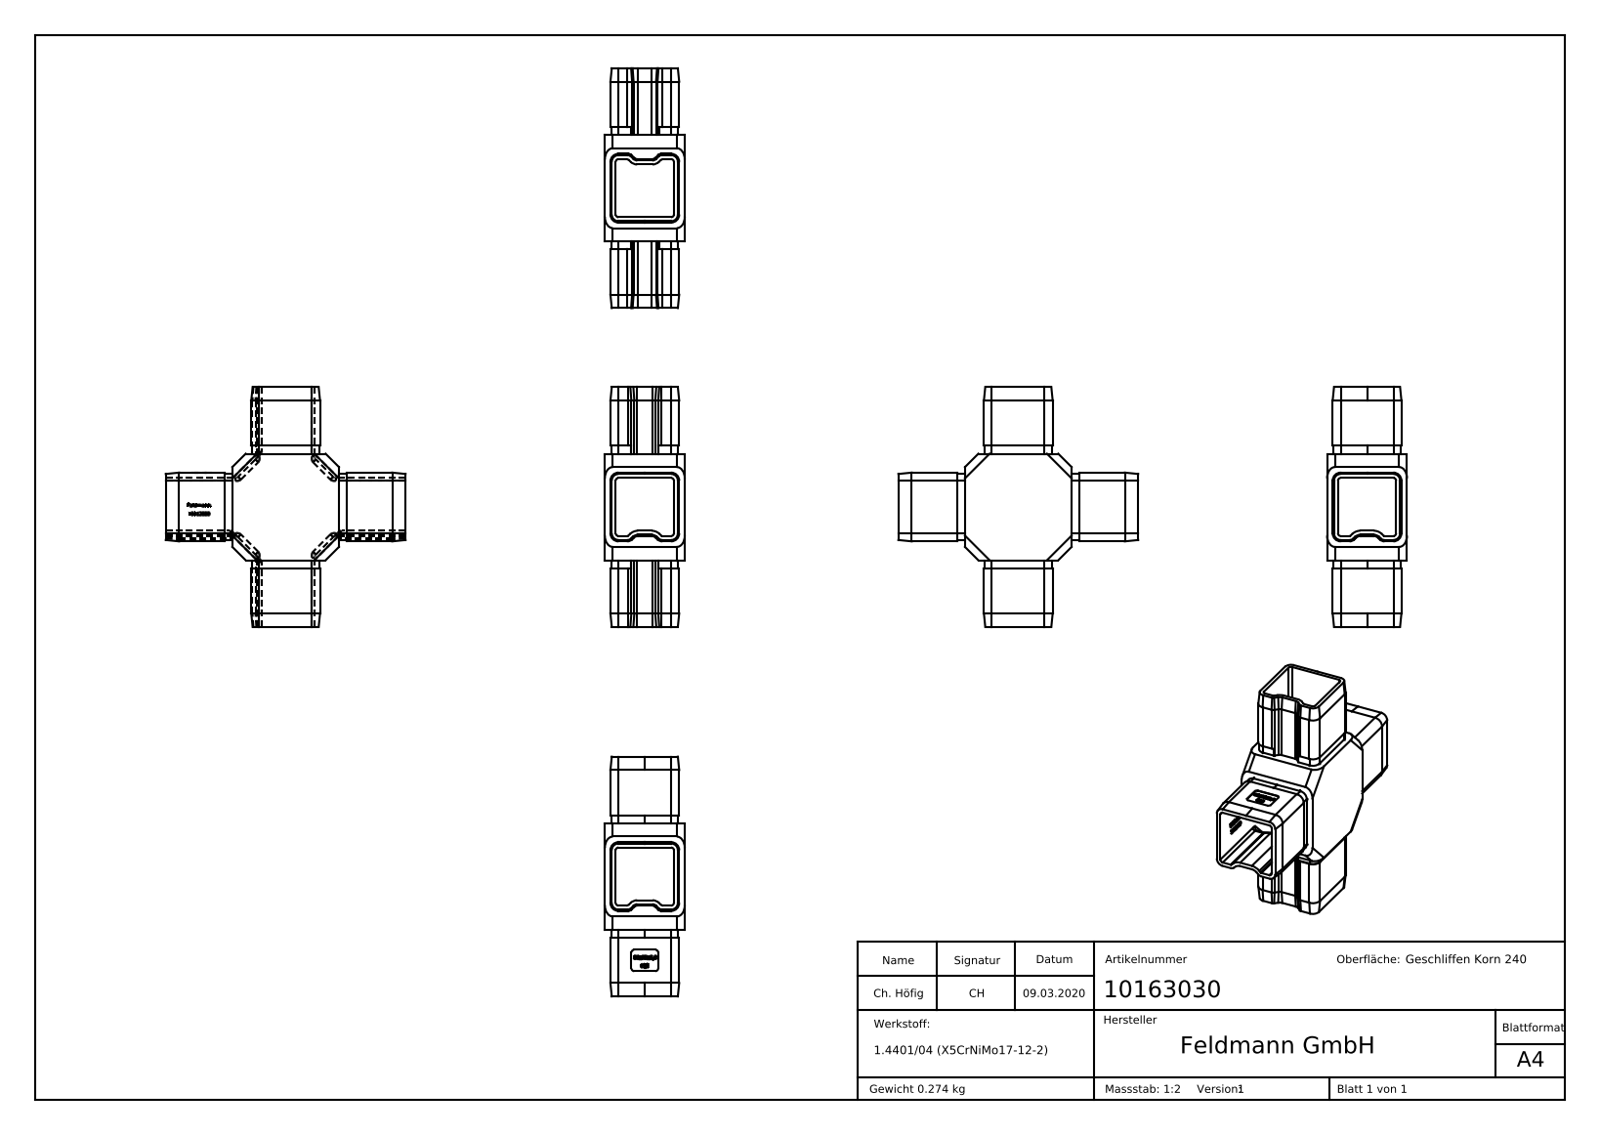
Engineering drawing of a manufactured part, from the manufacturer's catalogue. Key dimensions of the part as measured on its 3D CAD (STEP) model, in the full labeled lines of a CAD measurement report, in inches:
Part name (STEP PRODUCT): 10163030
STEP written by: SolidWorks 2015 (CONFIG_CONTROL_DESIGN)
Units: inches
Bodies: 1 solid, 731 faces (348 planar, 124 cylindrical, 259 other)
Overall size (bounding box): 3.543 × 3.543 × 1.181
Volume: 2.089 in³ · Surface area: 43.63 in²
Partial cylindrical surfaces — rounded edges, fillets, slot ends (radius × count): R0.059 ×34, R0.118 ×16, R0.039 ×12, R0.106 ×8, R0.097 ×4, R0.018 ×2, R0.138 ×2, R0.176 ×2
Main face-to-face distances: 0.079, 0.858, 0.937, 0.161, 1.02, 0.083, 1.098, 1.016, 1.181, 0.358
